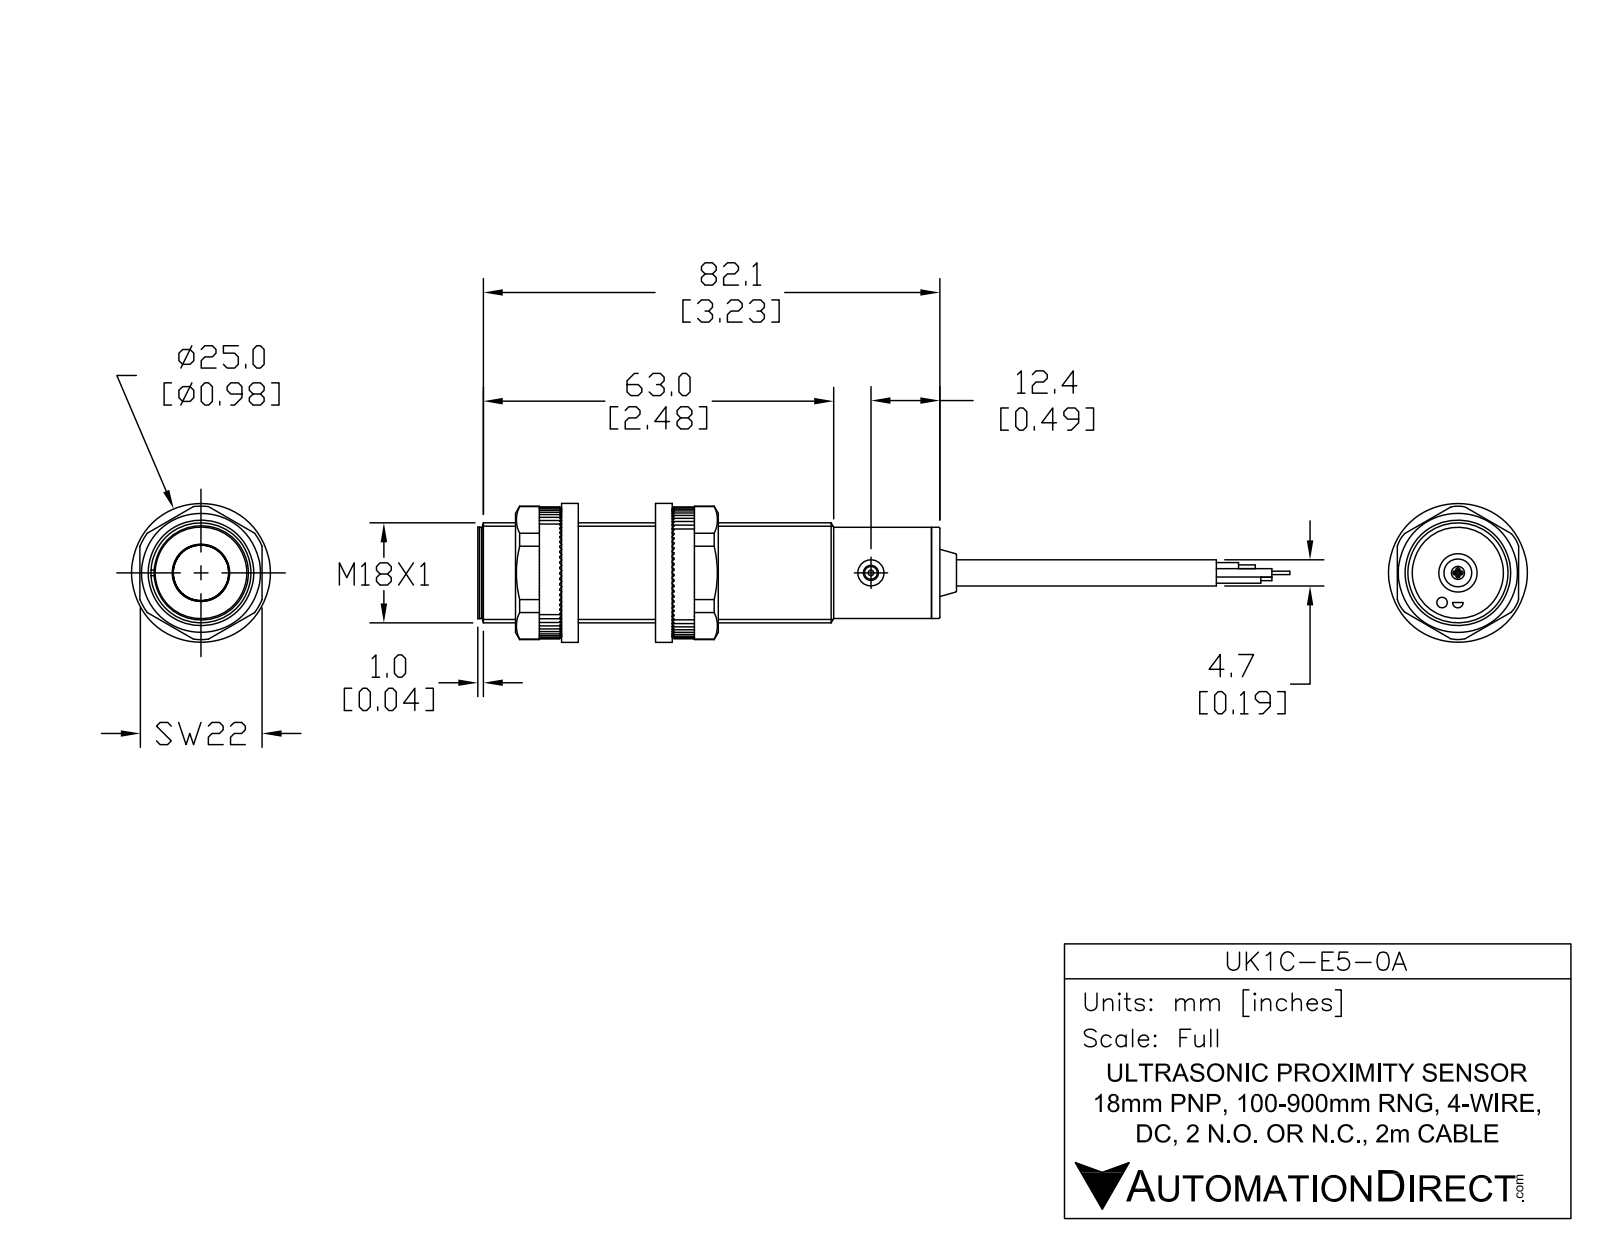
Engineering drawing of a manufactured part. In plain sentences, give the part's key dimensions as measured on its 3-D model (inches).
The part is named "UK1C-E5-0A". Its 3-D file was written by "SolidWorks 2017 (AUTOMOTIVE_DESIGN)". It is 6 solids with 55 faces: 17 planar, 24 cylindrical and 14 other. Overall it measures 4.832 by 0.709 by 0.709 inches. Its volume is 1.285 cubic inches and its surface area 10.69 square inches. Round holes: 2 of diameter 0.185, 1 of diameter 0.106. Round bosses or shafts: 1 of diameter 0.709, 1 of diameter 0.646, 1 of diameter 0.622, 1 of diameter 0.374, 1 of diameter 0.189, 1 of diameter 0.091. The main face-to-face distances are 3.193, 3.252, 0.059, 0.039, 3.232, 3.291, 0.041, 3.234, 3.293, 3.257.
